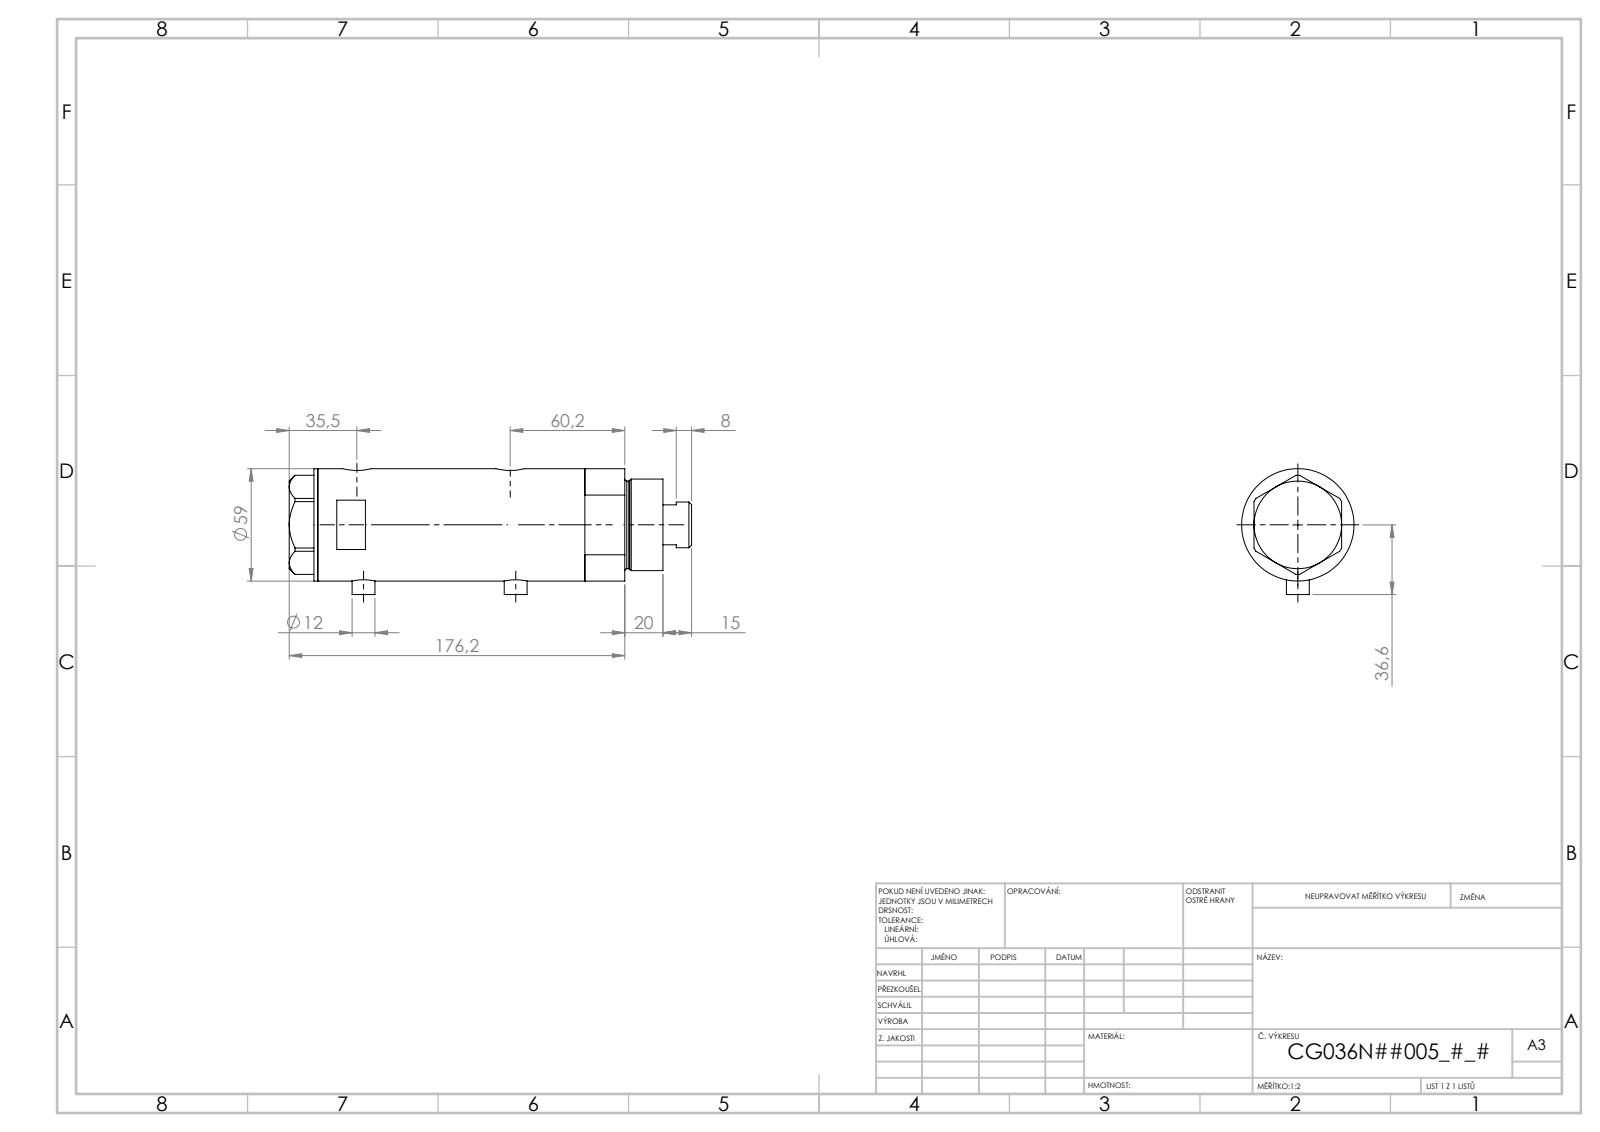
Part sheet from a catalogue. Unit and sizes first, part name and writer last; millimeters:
Units: millimetres
Overall size (bounding box): 168.42 × 60.1 × 59
Round holes (diameter × count): ⌀5 ×2, ⌀9.73 ×2, ⌀12.5 ×2, ⌀15 ×2, ⌀8.5 ×1, ⌀25 ×1, ⌀26.5 ×1, ⌀36 ×1, ⌀40 ×1, ⌀52 ×1
Round bosses / shafts (diameter × count): ⌀12 ×2, ⌀59 ×1, ⌀48 ×1, ⌀46 ×1, ⌀24 ×1
Main face-to-face distances: 62.34, 23.5, 38.84, 15, 38.5, 77.34, 153.42, 138.42, 114.92, 76.08
Hole centre spacings: 2.9, 3.5, 37.15, 40.05, 40.65, 43.55, 2.89, 2.91
Volume: 382 176 mm³ · Surface area: 83 778 mm²
Bodies: 4 solids, 126 faces (53 planar, 53 cylindrical, 20 other)
Part name (STEP PRODUCT): V270CG_MIDDLE; V270CG_VC; V270CG_BACK; V270CG_FRONT
STEP written by: SolidWorks 2019 (CONFIG_CONTROL_DESIGN)
